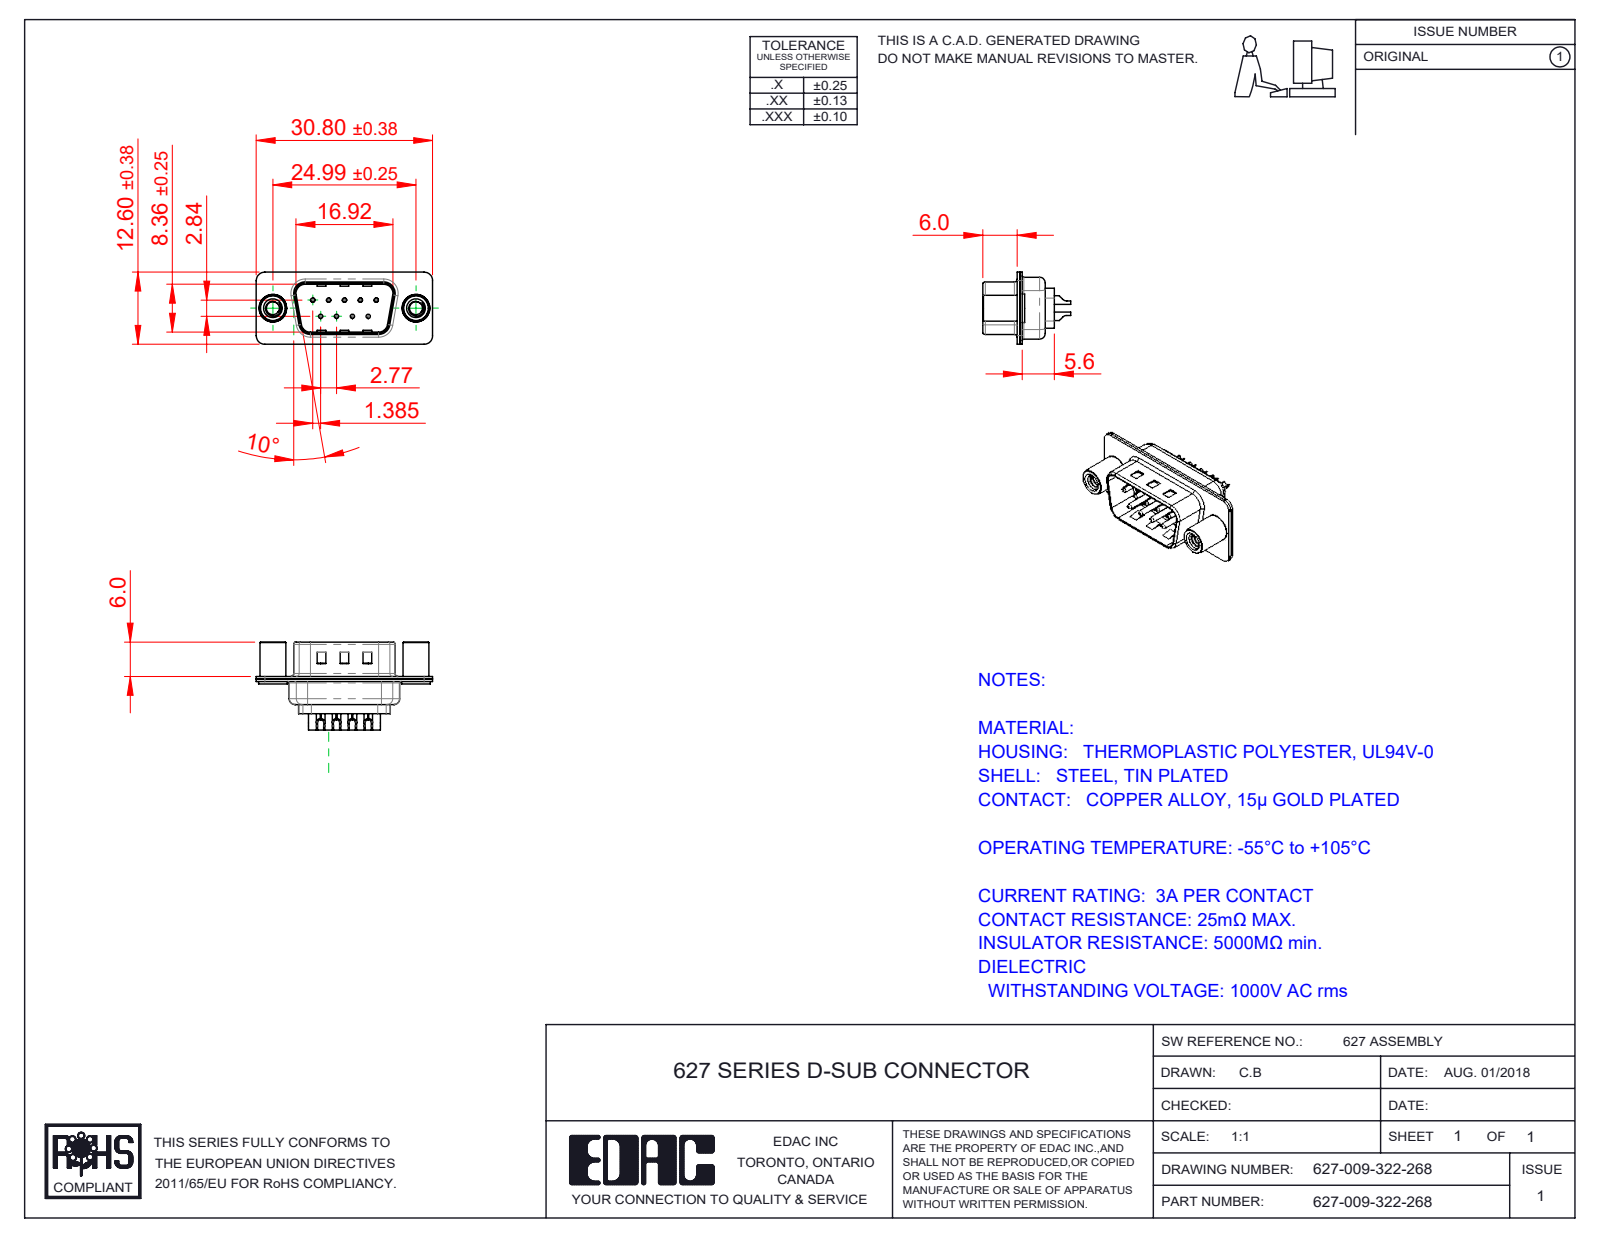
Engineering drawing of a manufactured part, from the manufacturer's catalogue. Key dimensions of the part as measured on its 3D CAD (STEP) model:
Part name (STEP PRODUCT): 627 Shell Rear_09 Contacts; 627 Shell Front_09 Contacts; 627 Housing_09 LP; 627-009-322-068 (+3 more)
STEP written by: SolidWorks 2020 (CONFIG_CONTROL_DESIGN)
Units: millimetres
Bodies: 14 solids, 914 faces (235 planar, 418 cylindrical, 261 other)
Overall size (bounding box): 30.8 × 15.35 × 12.6
Volume: 1 379 mm³ · Surface area: 4 147 mm²
Round holes (diameter × count): ⌀0.35 ×9, ⌀1.1 ×9, ⌀1.6 ×9, ⌀2.26 ×2, ⌀4 ×2, ⌀4.8 ×2
Round bosses / shafts (diameter × count): ⌀2 ×9, ⌀1.5 ×9, ⌀0.75 ×9, ⌀5 ×2, ⌀4.9 ×2, ⌀4.5 ×2
Partial cylindrical surfaces — rounded edges, fillets, slot ends (radius × count): R1.5 ×18, R2 ×12, R0.5 ×8, R1.6 ×8, R1 ×6, R0.25 ×4, R0.6 ×4, R0.65 ×4
Main face-to-face distances: 0.4, 0.45, 0.9, 0.82, 9.58, 1.4, 8.76, 0.5, 1.5, 6.5
Hole centre spacings: 3.16, 2.77, 5.54, 5.03, 5.04, 8.31, 7.48, 7.49
